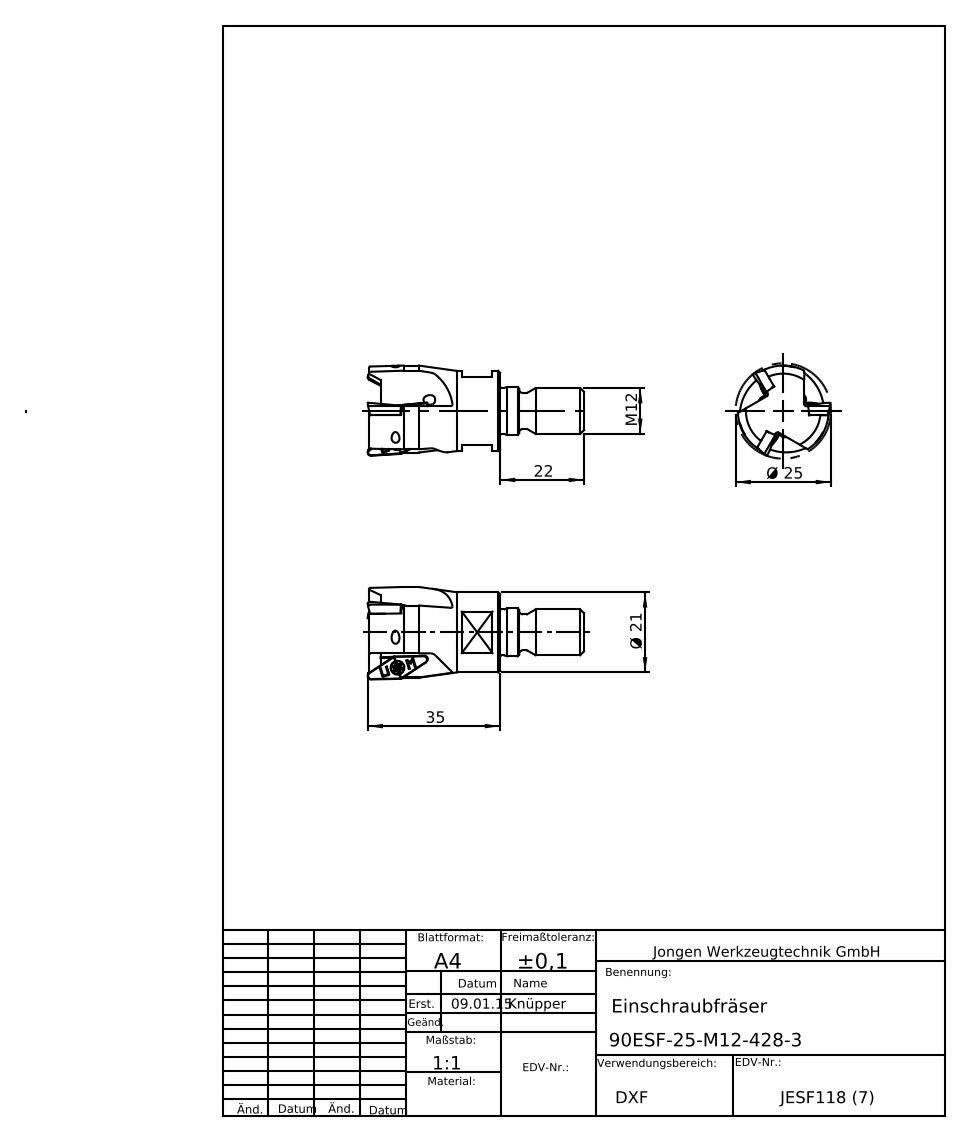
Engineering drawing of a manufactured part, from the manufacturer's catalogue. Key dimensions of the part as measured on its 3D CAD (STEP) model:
Part name (STEP PRODUCT): 90ESF_25_M12_428_3
STEP written by: SolidWorks 2016 (AUTOMOTIVE_DESIGN)
Units: millimetres
Bodies: 1 solid, 140 faces (52 planar, 37 cylindrical, 51 other)
Overall size (bounding box): 56.99 × 24.95 × 24.94
Volume: 14 201 mm³ · Surface area: 5 003 mm²
Round holes (diameter × count): ⌀2.5 ×3, ⌀3 ×1
Round bosses / shafts (diameter × count): ⌀21 ×1, ⌀12.5 ×1, ⌀12.1 ×1, ⌀12 ×1, ⌀9.4 ×1
Partial cylindrical surfaces — rounded edges, fillets, slot ends (radius × count): R0.5 ×6, R0.62 ×3, R2 ×3, R11.9 ×1
Main face-to-face distances: 31.3, 18, 53.3, 22, 10.28, 7.72, 21.3, 10, 32, 29.3
